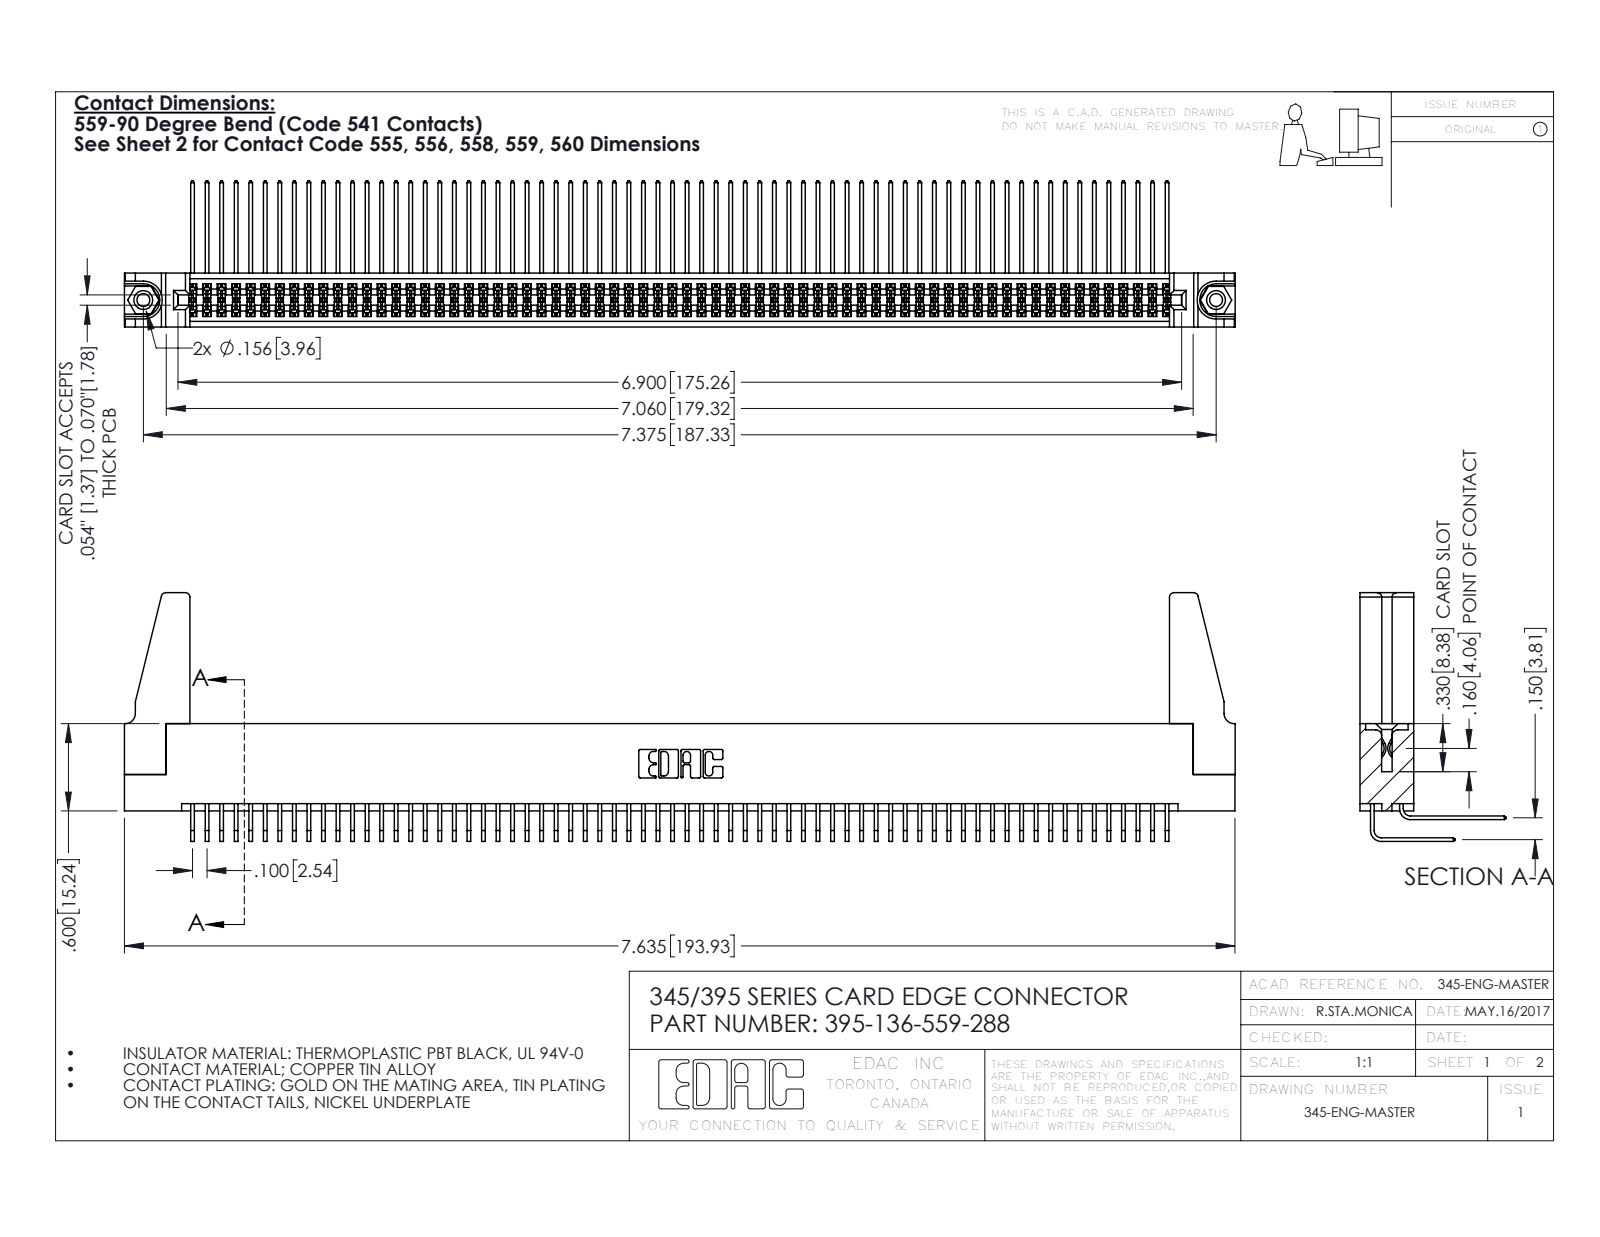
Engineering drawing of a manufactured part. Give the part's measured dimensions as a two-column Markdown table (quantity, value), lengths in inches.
| quantity | value |
| --- | --- |
| part name | 345-250-001_345-250-001-102; 345 Part_Flush Mounting Lugs - 0.156 Dia-TH; 345-292-001_558 559 Tail - 1; 345-220-078_345-220-088 (+2 more) |
| STEP written by | SolidWorks 2016 (CONFIG_CONTROL_DESIGN) |
| units | inches |
| bodies | 141 solids, 7322 faces (4912 planar, 2394 cylindrical, 16 other) |
| overall size | 7.636 × 1.709 × 1.005 |
| volume | 1.411 in³ |
| surface area | 56.86 in² |
| round holes (diameter × count) | 0.089 × 2, 0.125 × 2, 0.156 × 2, 0.064 × 1 |
| round bosses / shafts (diameter × count) | 0.155 × 2 |
| partial cylindrical surfaces (radius × count) | 0.006 × 271, 0.01 × 22, 0.03 × 8, 0.007 × 6, 0.031 × 6, 0.026 × 3, 0.014 × 2, 0.019 × 2 |
| main face-to-face distances | 0.072, 0.298, 0.37, 0.2, 0.098, 0.272, 0.025, 0.225, 0.175, 0.15 |
| hole center spacings | 0.27, 7.139, 7.375 |
